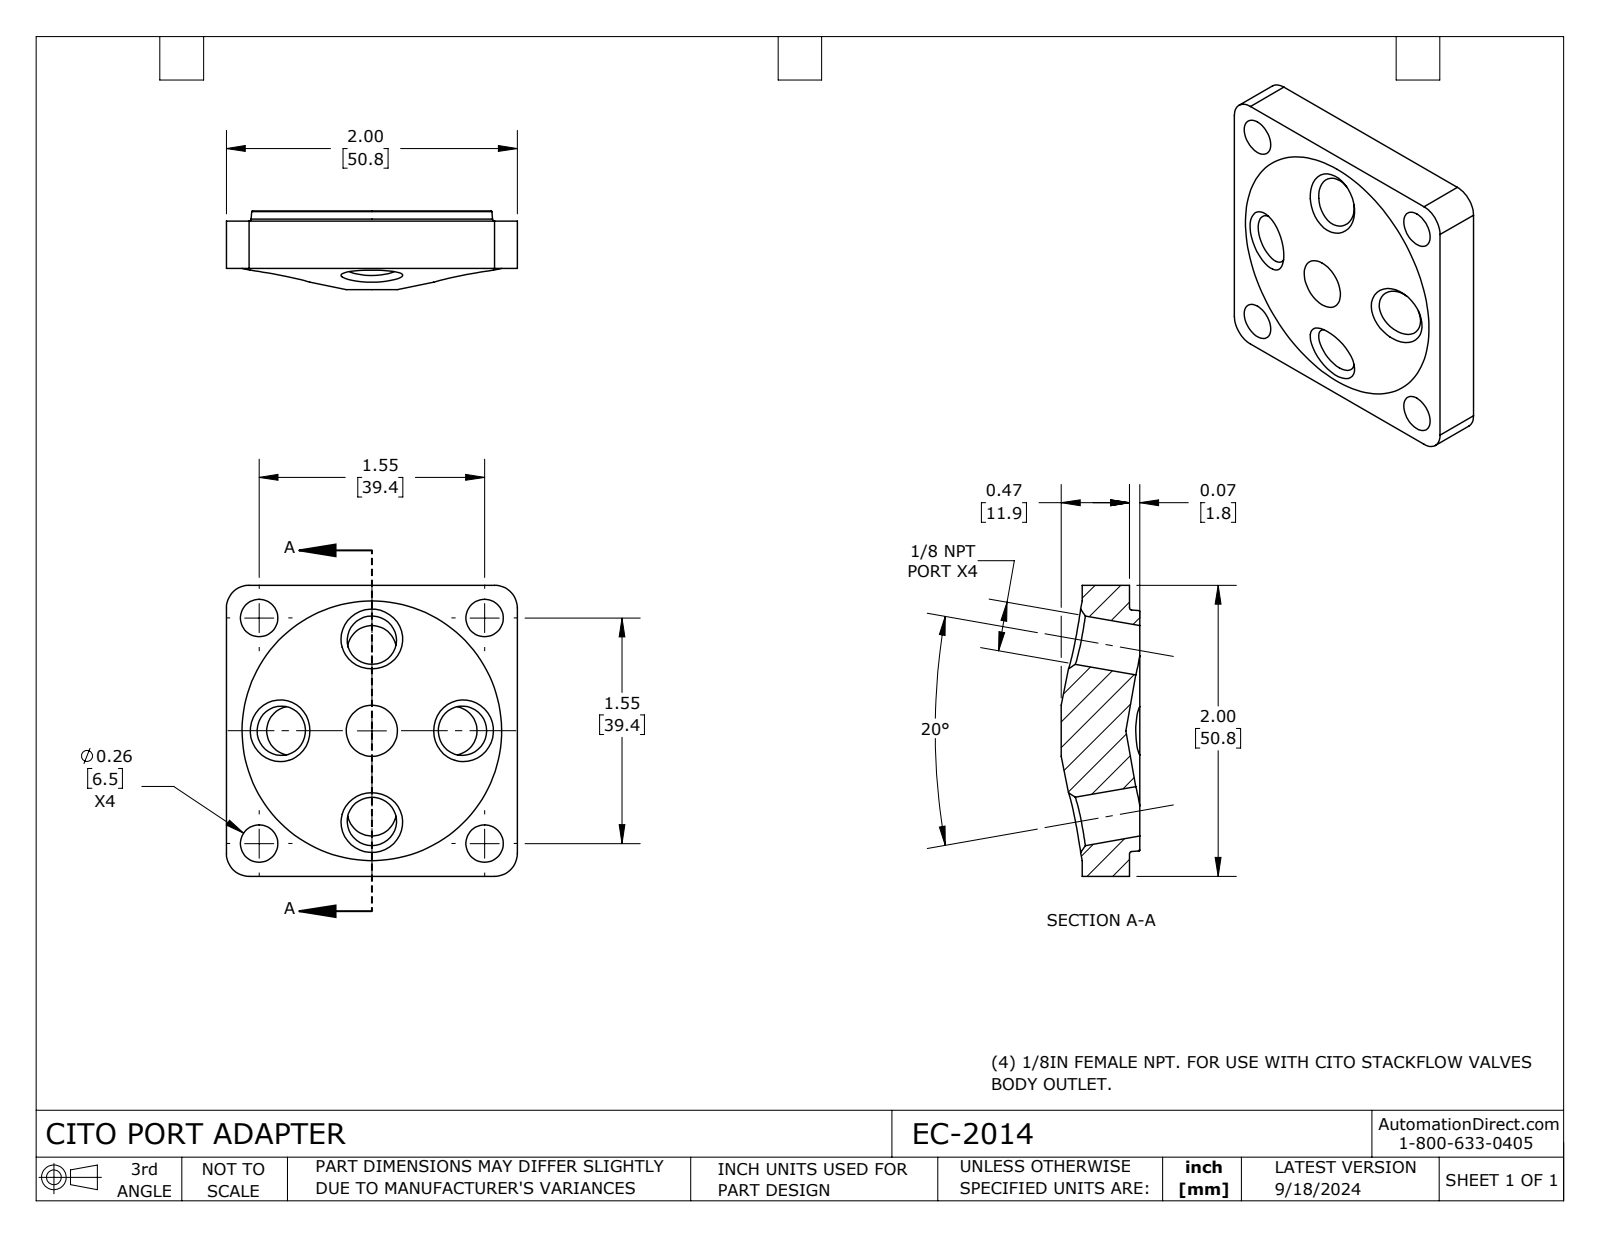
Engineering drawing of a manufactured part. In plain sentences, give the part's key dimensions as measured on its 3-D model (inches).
The part is named "EC-2014". Its 3-D file was written by "SolidWorks 2023 (CONFIG_CONTROL_DESIGN)". It is 1 solid with 46 faces: 8 planar, 20 cylindrical and 18 other. Overall it measures 2 by 2 by 0.54 inches. Its volume is 1.331 cubic inches and its surface area 12.54 square inches. Round holes: 4 of diameter 0.257, 4 of diameter 0.339. Partial cylindrical surfaces (rounded edges, fillets, slot ends): 4 of radius 0.156. The main face-to-face distances are 0.325, 2, 0.395, 0.07, 0.145, 0.47, 0.54. The hole center spacings are 1.55, 2.191.
